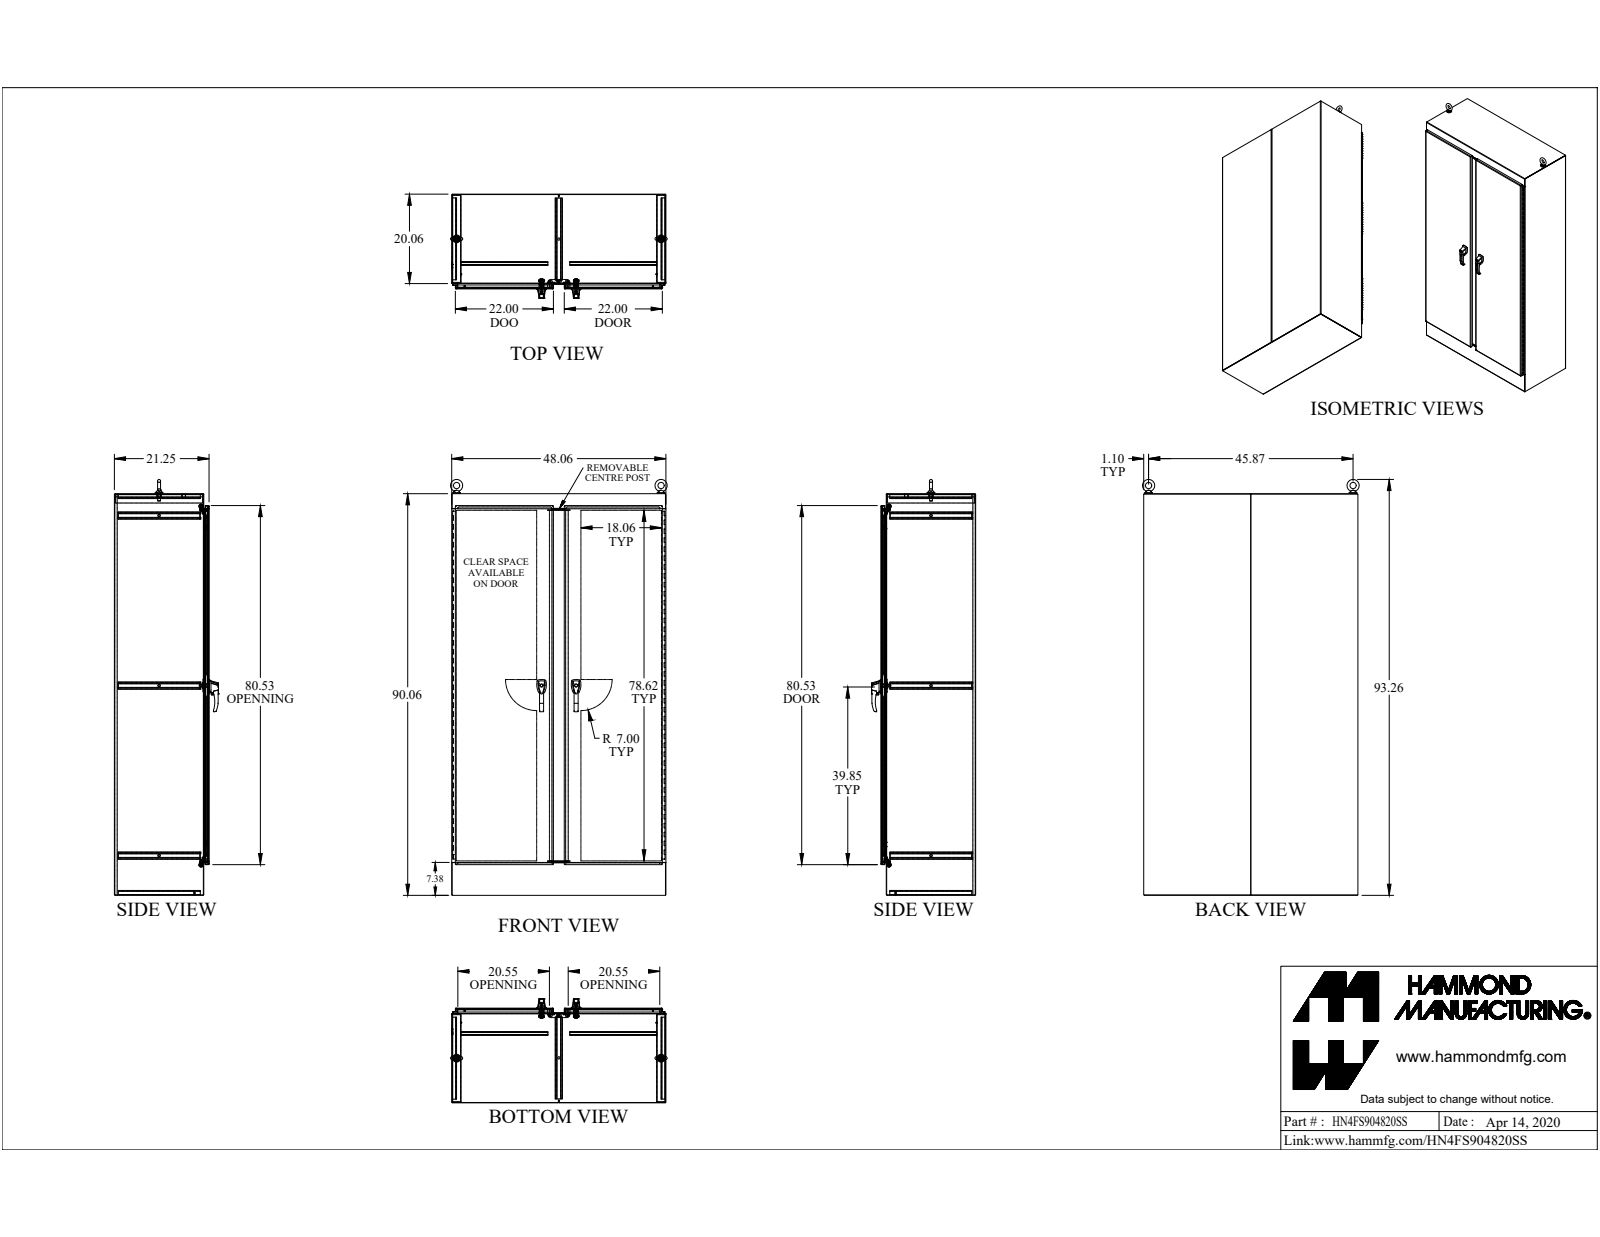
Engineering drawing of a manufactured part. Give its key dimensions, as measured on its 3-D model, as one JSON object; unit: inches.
{"part_name": "HN4FS904820SS", "step_written_by": "SolidWorks 2019 (CONFIG_CONTROL_DESIGN)", "units": "inches", "bodies": {"solids": 106, "faces": 3187, "planar": 1671, "cylindrical": 1270, "other": 246}, "overall_size": [93.256, 48.604, 23.362], "volume_in3": 1675, "surface_area_in2": 35367, "round_holes": [[0.304, 26], [0.35, 8], [0.25, 7], [0.5, 7], [0.257, 4], [0.28, 4], [0.281, 4], [0.313, 4], [0.39, 4], [0.413, 4], [0.201, 3], [0.313, 3]], "round_bosses_or_shafts": [[1, 4], [0.75, 4], [0.63, 4], [0.625, 4], [0.44, 4], [0.37, 4], [0.313, 4], [0.25, 4]], "partial_cylinders_radius": [[0.043, 54], [0.138, 48], [0.5, 33], [0.018, 32], [0.1, 28], [0.125, 27], [0.06, 24], [0.036, 16]], "face_to_face_distances": [0.095, 21.152, 21.057, 47.965, 21.247, 47.87, 89.965, 48.06, 1.187, 19.965], "hole_center_spacings": [6, 46.715, 12, 47.857, 18, 49.702, 24, 52.176]}
